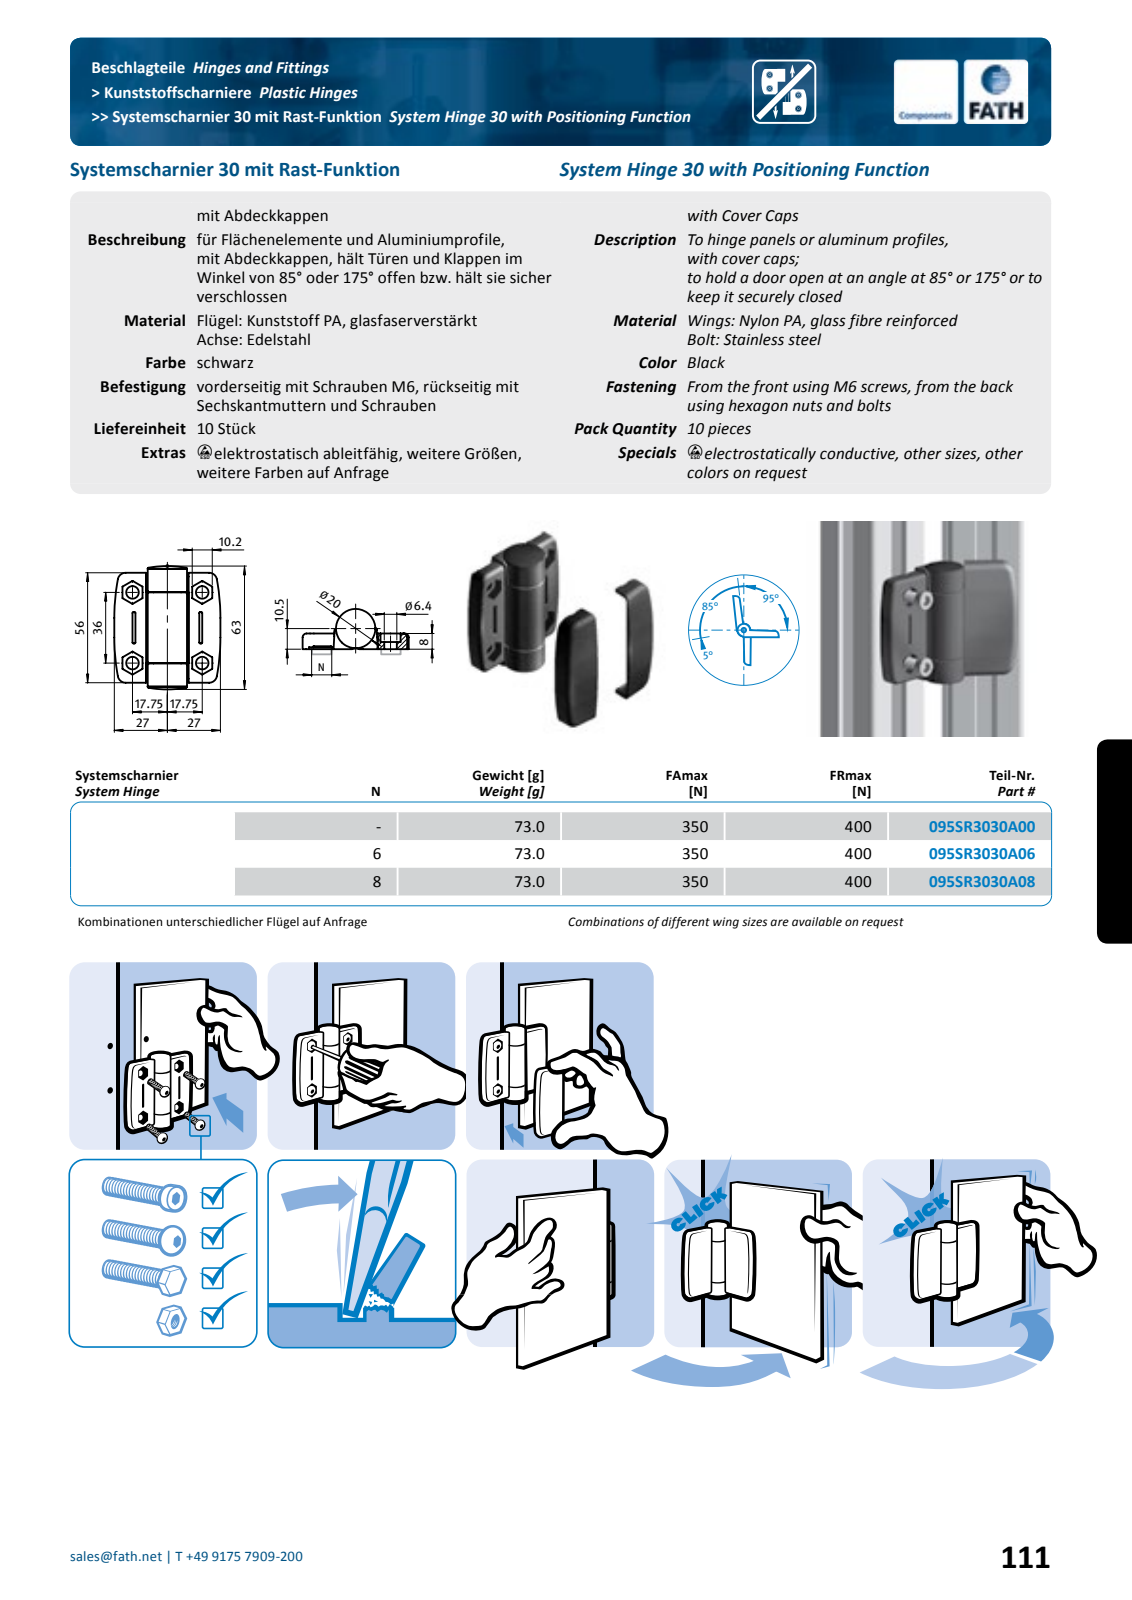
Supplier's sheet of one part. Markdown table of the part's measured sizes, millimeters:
| quantity | value |
| --- | --- |
| part name | fath_095sr3030a08_1; fath_095sr3030a08_2; fath_095sr3030a08_3; fath_095sr3030a08_4 (+8 more) |
| STEP written by | Spatial InterOp 3D (automotive_design) |
| units | millimeters |
| bodies | 13 solids, 1162 faces (346 planar, 348 cylindrical, 468 other) |
| overall size | 62.8 × 58 × 23.5 |
| volume | 34 615 mm³ |
| surface area | 31 178 mm² |
| round holes (diameter × count) | 6.4 × 4, 5.2 × 1, 5.3 × 1, 14 × 1 |
| round bosses / shafts (diameter × count) | 20 × 1, 13.8 × 1, 8 × 1, 5 × 1 |
| partial cylindrical surfaces (radius × count) | 0.2 × 54, 0.5 × 40, 0.3 × 6, 1.5 × 6, 2.5 × 6, 2 × 4, 4 × 4, 4.2 × 4 |
| main face-to-face distances | 8, 12, 48.2, 2, 48, 11.8, 36.2, 4.35, 1, 60 |
| hole center spacings | 35.5, 36, 50.56 |
